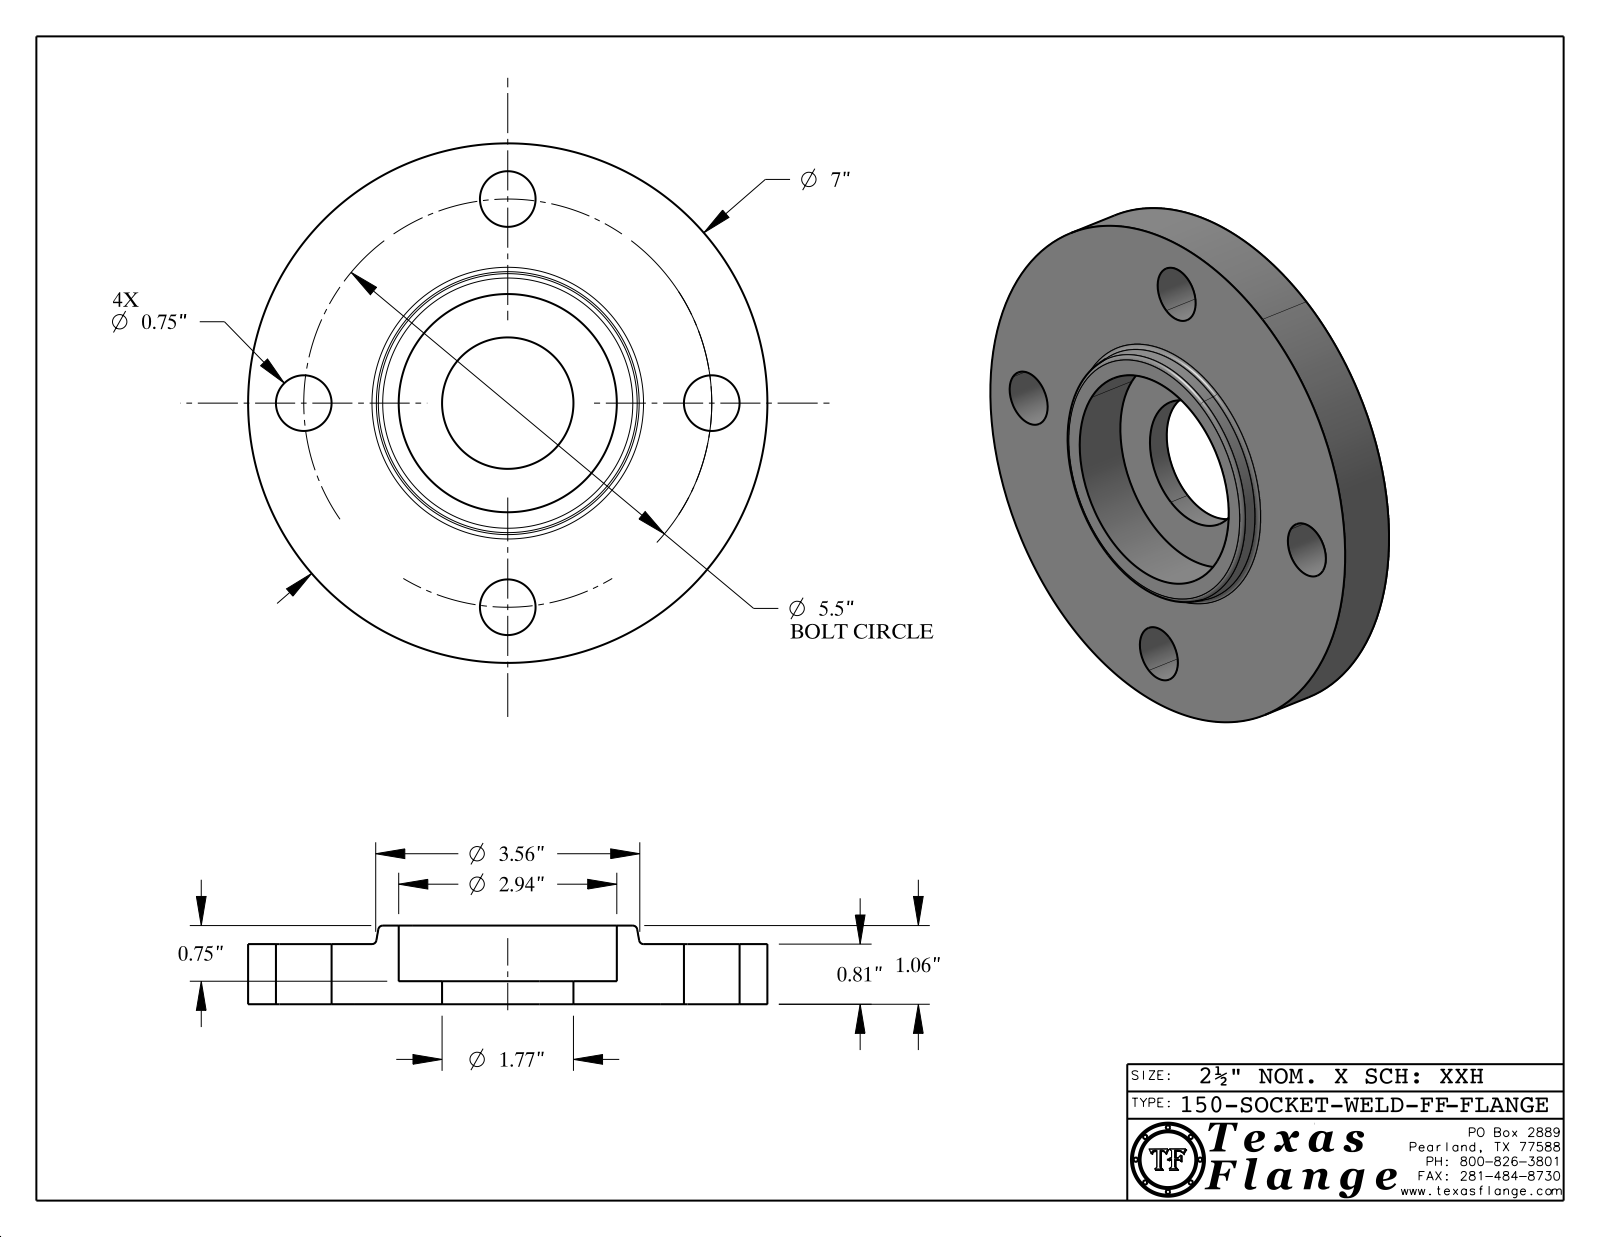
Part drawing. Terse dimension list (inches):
name: 150-SOCKET-WELD-FF
written by: CATIA V5 STEP AP214 (AUTOMOTIVE_DESIGN)
unit: in
bodies: 1 solid, 410 faces (370 planar, 34 cylindrical, 6 other)
size: 7 × 7 × 1.06
volume: 26.31 in³; area: 104.6 in²
holes: 4× ⌀0.75, 1× ⌀0.495, 1× ⌀1.771, 1× ⌀2.94
bosses: 8× ⌀0.03, 1× ⌀7, 1× ⌀0.39
face distances: 0.81, 0.31, 0.5, 1.06, 0.75, 0.25, 0.795, 0.485, 0.015, 0.265
hole spacings: 2.75, 3.889, 2.105, 5.081, 5.5
